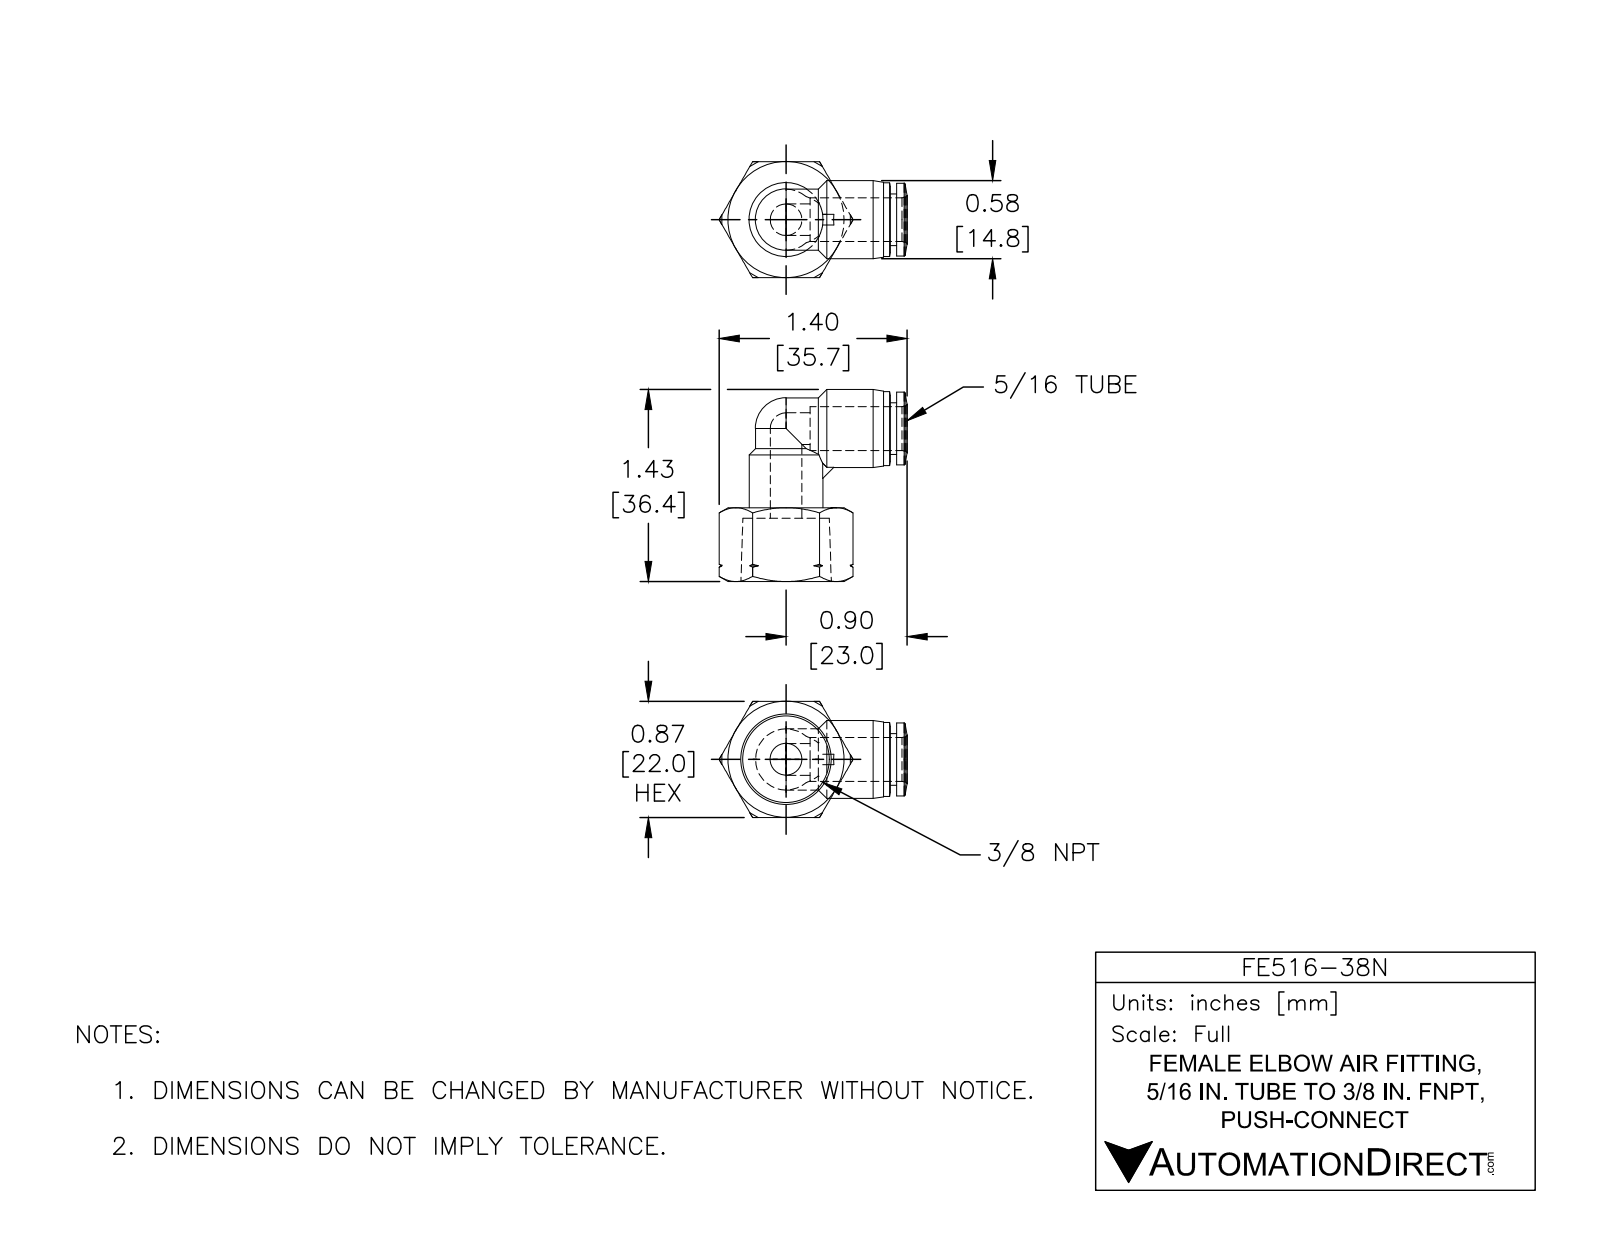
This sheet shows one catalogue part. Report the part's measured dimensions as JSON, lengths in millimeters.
{"part_name": "FE516-38N", "step_written_by": "SolidWorks 2015 (CONFIG_CONTROL_DESIGN)", "units": "millimeters", "bodies": {"solids": 1, "faces": 87, "planar": 16, "cylindrical": 21, "other": 50}, "overall_size": [36.4, 35.7, 22], "volume_mm3": 6900, "surface_area_mm2": 5019, "round_holes": [[6, 2], [8.3, 1]], "round_bosses_or_shafts": [[14, 2], [14.8, 1], [13.8, 1], [11.6, 1], [9.8, 1]], "partial_cylinders_radius": [[5.8, 1]], "face_to_face_distances": [22, 2, 12, 14, 1.2, 15.2, 16.4, 10, 13.9, 1.2]}
